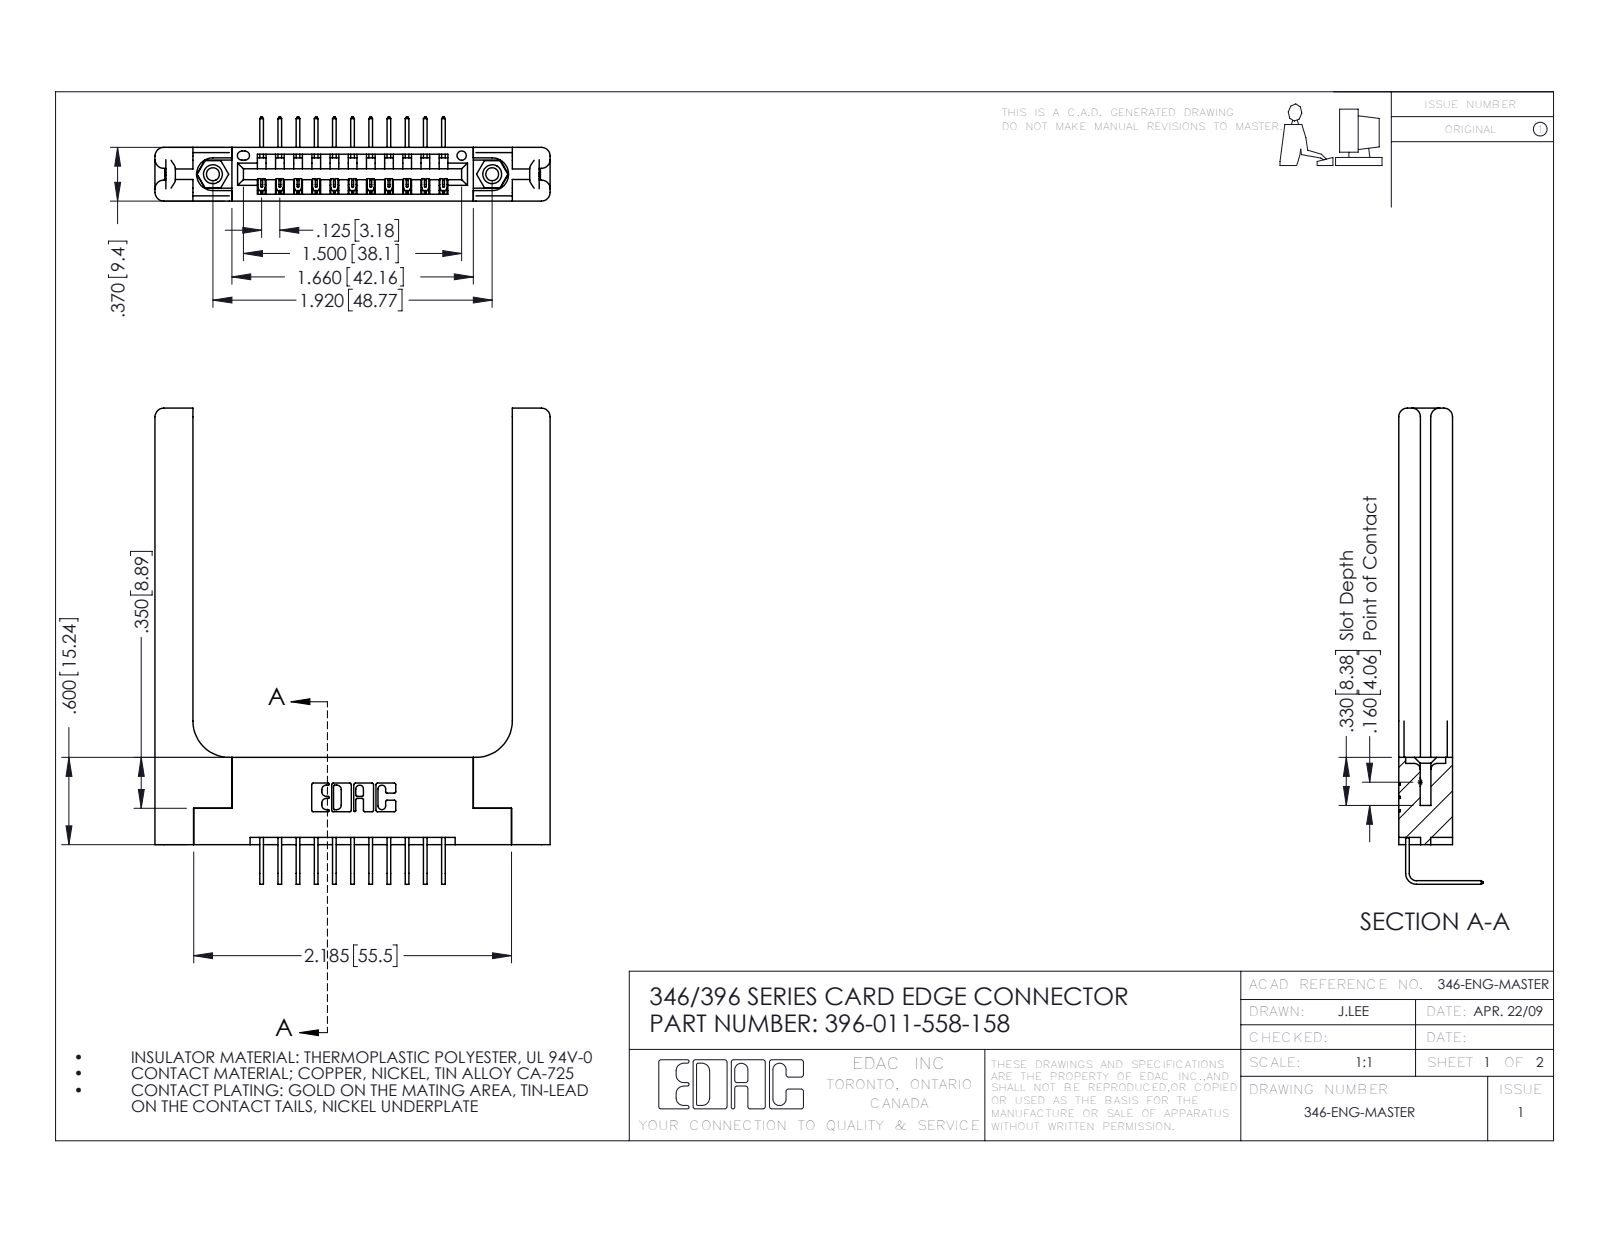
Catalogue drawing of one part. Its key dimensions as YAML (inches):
part_name: "345-292-001_558 Tail - 2; 346 Part_Flush Mounting Lugs - 0.156 Dia-TH; 345-250-001_345-250-001-102; 396-011-558-158 (+1 more)"
step_written_by: "SolidWorks 2016 (CONFIG_CONTROL_DESIGN)"
units: inches
bodies: {solids: 16, faces: 1038, planar: 686, cylindrical: 292, other: 60}
overall_size: [3.273, 2.716, 0.58]
volume: 0.851
surface_area: 20.28
round_holes:
  - {diameter: 0.089, count: 2}
  - {diameter: 0.125, count: 2}
  - {diameter: 0.156, count: 2}
  - {diameter: 0.064, count: 1}
round_bosses_or_shafts:
  - {diameter: 0.155, count: 2}
partial_cylinders:
  - {radius: 0.006, count: 22}
  - {radius: 0.01, count: 22}
  - {radius: 0.06, count: 16}
  - {radius: 0.007, count: 6}
  - {radius: 0.031, count: 6}
  - {radius: 0.026, count: 3}
  - {radius: 0.03, count: 2}
  - {radius: 0.031, count: 2}
face_to_face_distances: [0.37, 0.15, 0.072, 0.148, 0.22, 0.322, 0.25, 0.048, 0.102, 0.173]
hole_center_spacings: [0.246, 1.715, 1.92]
